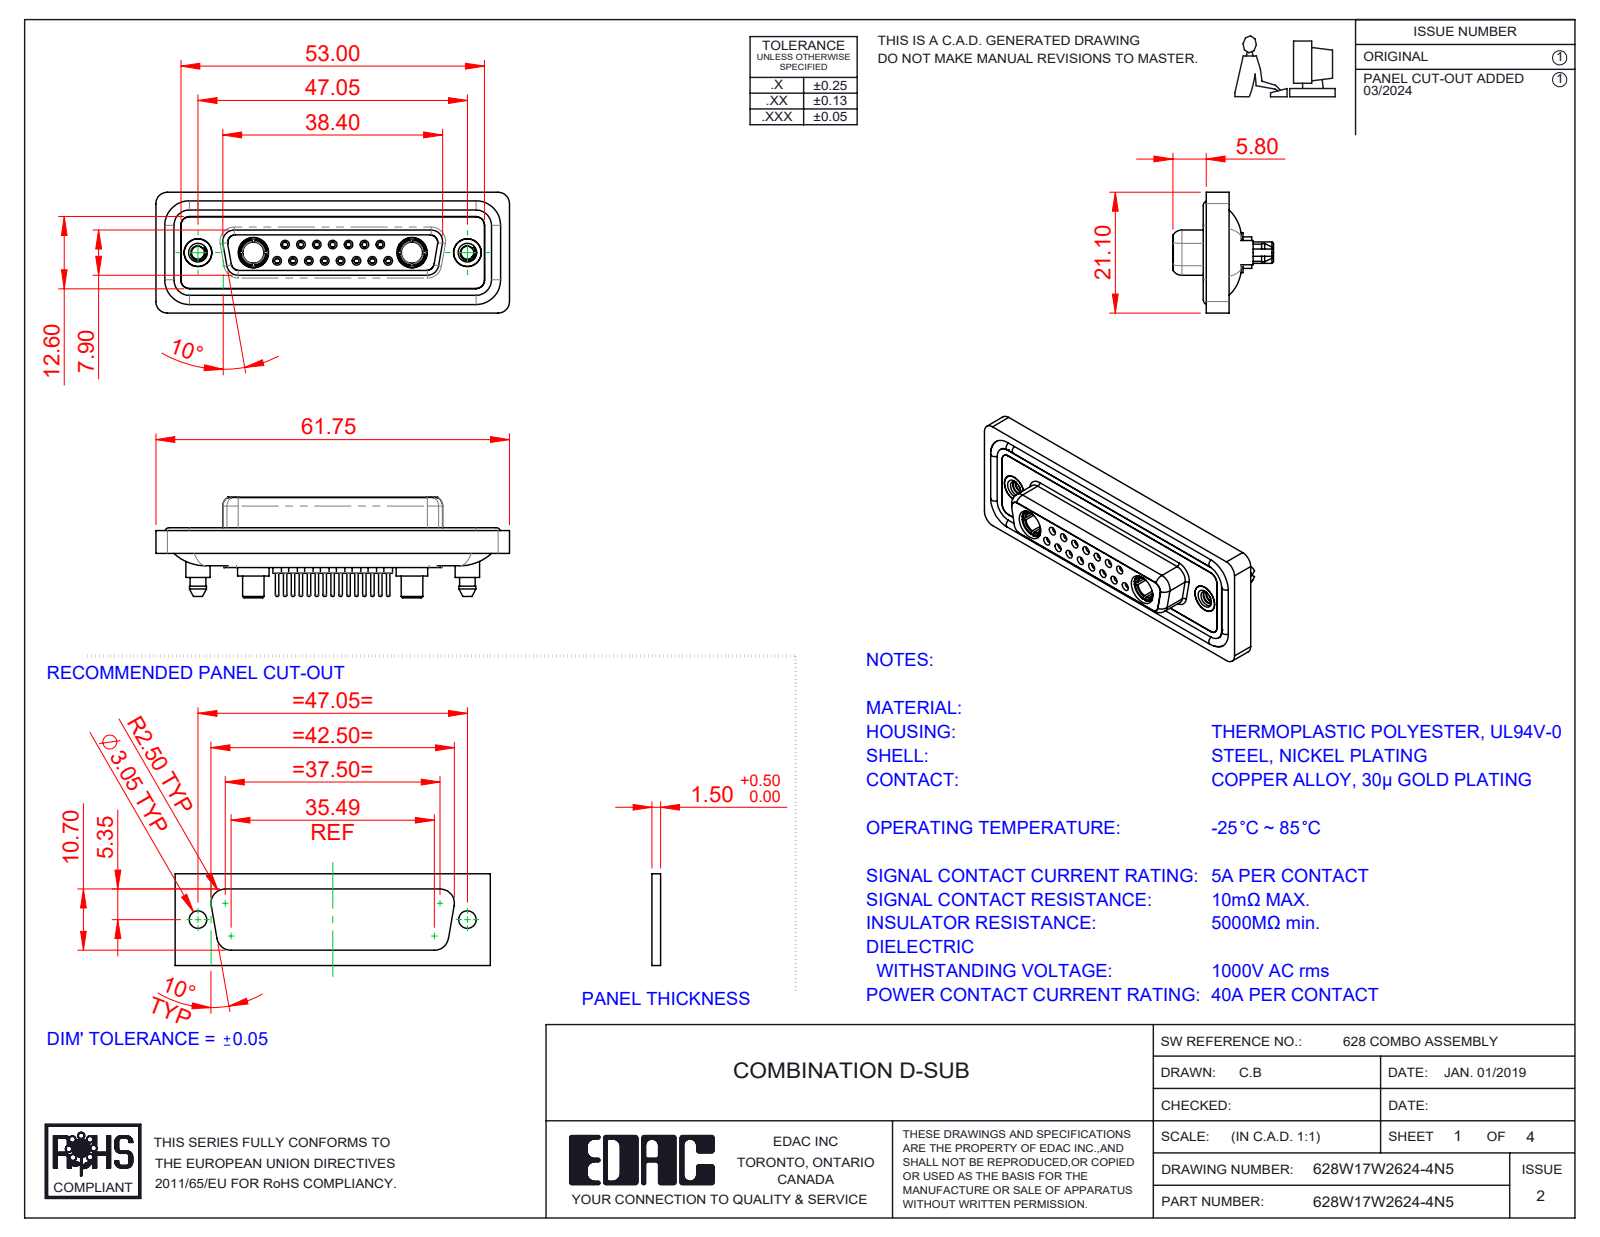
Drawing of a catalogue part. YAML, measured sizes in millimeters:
part_name: "628Combo Waterproof Housing_25 Contacts; 628W17W2624-4N5; 628Combo Contact Row 2_24; 628Combo Threaded Boardlock_5 (+5 more)"
step_written_by: "SolidWorks 2023 (CONFIG_CONTROL_DESIGN)"
units: millimeters
bodies: {solids: 26, faces: 1409, planar: 404, cylindrical: 551, other: 454}
overall_size: [61.75, 21.1, 17.55]
volume: 8495
surface_area: 14210
round_holes:
  - {diameter: 0.9, count: 15}
  - {diameter: 1.1, count: 15}
  - {diameter: 1.5, count: 15}
  - {diameter: 2, count: 15}
  - {diameter: 1.6, count: 8}
  - {diameter: 1.7, count: 7}
  - {diameter: 4.85, count: 4}
  - {diameter: 2.26, count: 2}
  - {diameter: 3.7, count: 2}
  - {diameter: 4, count: 2}
  - {diameter: 4.05, count: 2}
  - {diameter: 5, count: 2}
round_bosses_or_shafts:
  - {diameter: 2.2, count: 15}
  - {diameter: 0.6, count: 15}
  - {diameter: 1.6, count: 11}
  - {diameter: 5.5, count: 2}
  - {diameter: 5.4, count: 2}
  - {diameter: 5.2, count: 2}
  - {diameter: 4.96, count: 2}
  - {diameter: 4.95, count: 2}
partial_cylinders:
  - {radius: 1.5, count: 24}
  - {radius: 2, count: 18}
  - {radius: 1.6, count: 10}
  - {radius: 1.35, count: 8}
  - {radius: 0.25, count: 4}
  - {radius: 0.5, count: 4}
  - {radius: 0.6, count: 4}
  - {radius: 0.65, count: 4}
face_to_face_distances: [0.4, 1.8, 7.45, 5.65, 6.6, 0.5, 7.05, 1.6, 2.9, 1.1]
hole_center_spacings: [3.16, 2.77, 8.31, 5.54, 5.03, 5.04, 7.49, 11.08]
